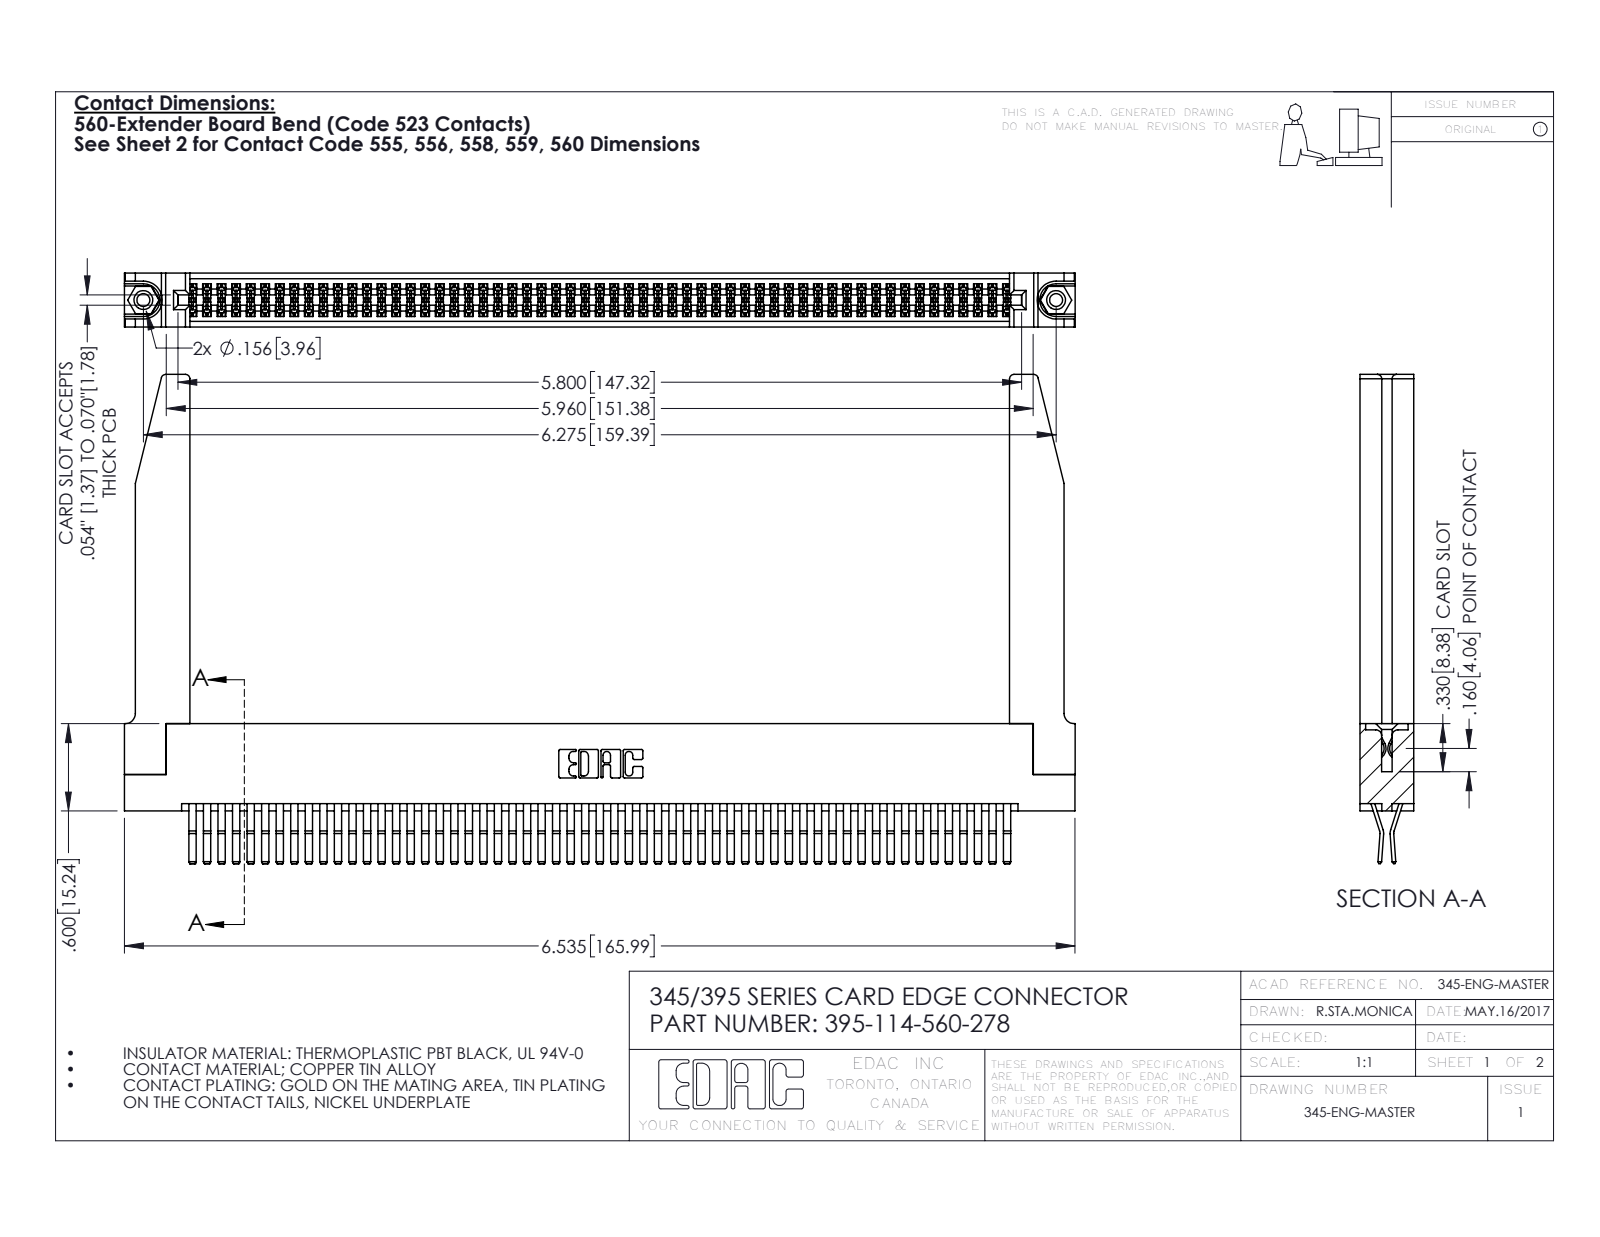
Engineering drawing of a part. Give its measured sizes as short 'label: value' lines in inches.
name: 345 Part_Flush Mounting Lugs - 0.156 Dia-TH; 345-250-001_345-250-001-102; 395-114-560-278; 345-220-078_345-220-078 (+1 more)
written by: SolidWorks 2016 (CONFIG_CONTROL_DESIGN)
unit: in
bodies: 119 solids, 6288 faces (3984 planar, 2252 cylindrical, 52 other)
size: 6.536 × 3.362 × 0.37
volume: 1.512 in³; area: 53.01 in²
holes: 2× ⌀0.089, 2× ⌀0.125, 2× ⌀0.156, 1× ⌀0.064
bosses: 2× ⌀0.155
rounds: 171× R0.006, 22× R0.01, 8× R0.03, 6× R0.007, 6× R0.031, 3× R0.026, 2× R0.01, 2× R0.014
face distances: 0.072, 0.37, 0.298, 0.025, 0.2, 0.098, 0.272, 0.225, 0.175, 0.148
hole spacings: 0.27, 6.039, 6.275
